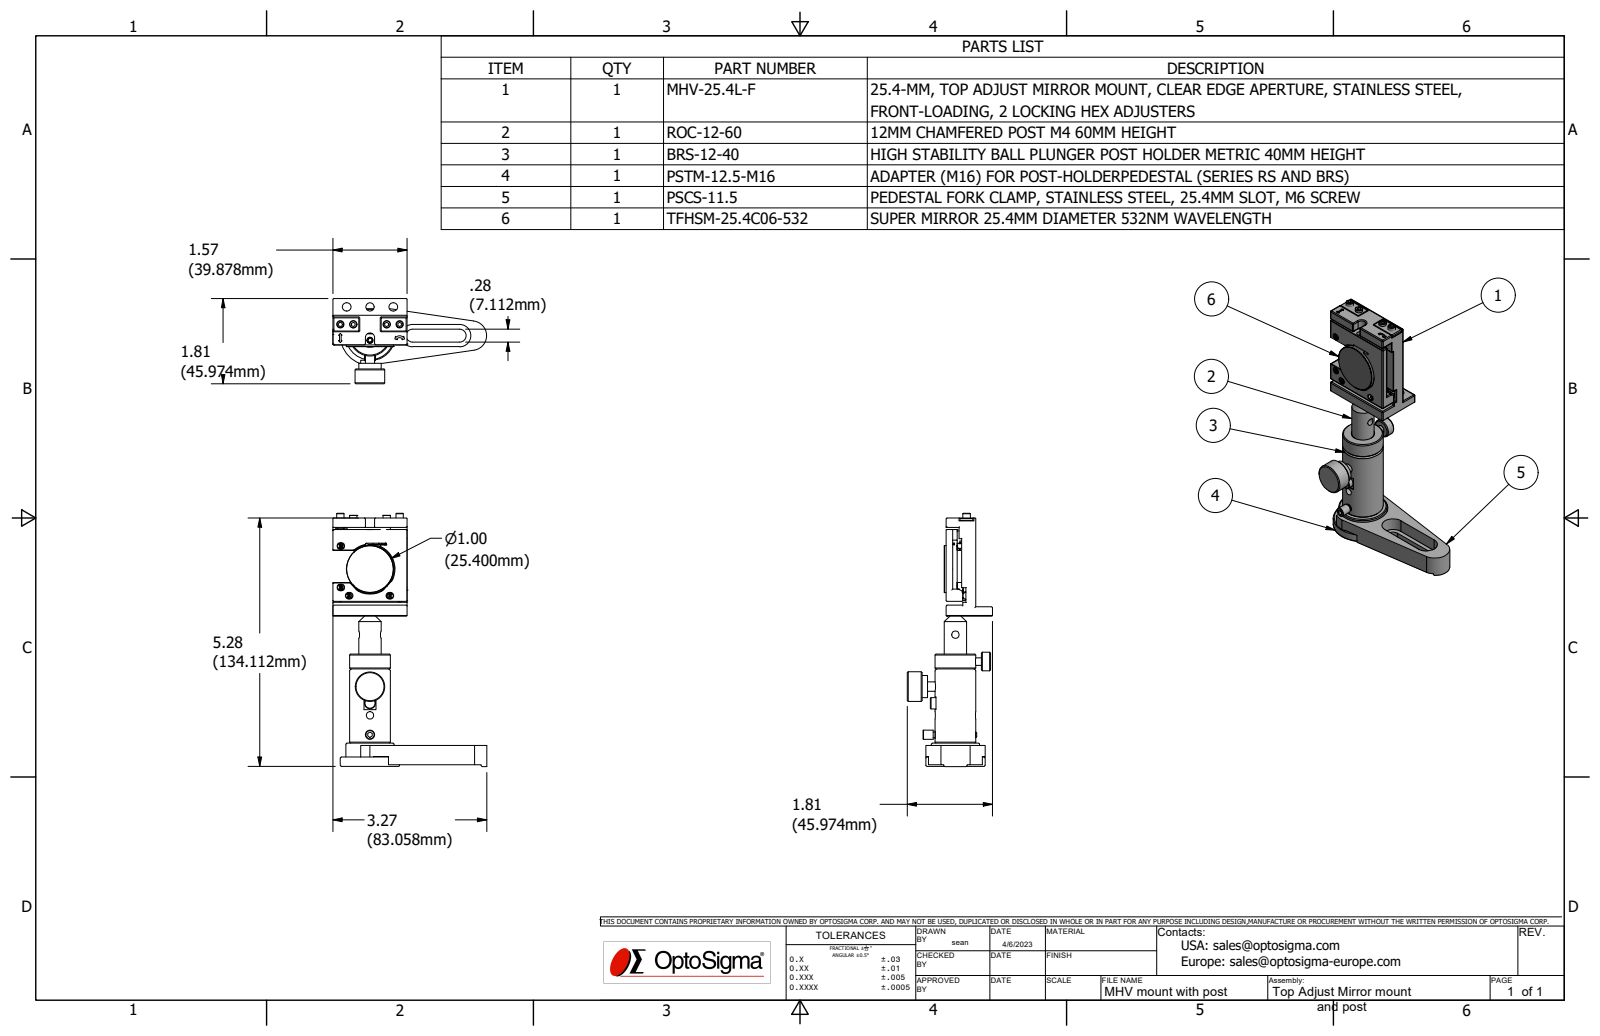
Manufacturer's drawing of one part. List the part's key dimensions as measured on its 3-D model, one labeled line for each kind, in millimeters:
Part name (STEP PRODUCT): Top adjust mirror holder and post; MHV25.4L-M02-21001-S01; MHV25.4L-M02-21001-S02; MHV25.4L-M02-21001-S03 (+7 more)
STEP written by: Autodesk Inventor 2022 (AUTOMOTIVE_DESIGN)
Units: millimetres
Bodies: 11 solids, 1036 faces (524 planar, 296 cylindrical, 216 other)
Overall size (bounding box): 136.7 × 83 × 46
Volume: 59 298 mm³ · Surface area: 33 793 mm²
Round holes (diameter × count): ⌀4 ×5, ⌀1 ×3, ⌀1.5 ×2, ⌀2 ×2, ⌀3.8 ×2, ⌀4.13 ×2, ⌀4.2 ×2, ⌀5.5 ×2, ⌀7 ×2, ⌀1.6 ×1, ⌀3 ×1, ⌀3.2 ×1
Round bosses / shafts (diameter × count): ⌀4 ×6, ⌀2.6 ×4, ⌀5 ×3, ⌀16 ×2, ⌀6.8 ×2, ⌀5.4 ×2, ⌀3 ×2, ⌀32 ×1
Partial cylindrical surfaces — rounded edges, fillets, slot ends (radius × count): R0.5 ×61, R0.2 ×51, R1.5 ×10, R4 ×9, R1 ×6, R2.25 ×4, R3.5 ×2, R6 ×2
Main face-to-face distances: 5, 16, 1, 6, 7, 11, 10, 9, 4, 8
Hole centre spacings: 6.95, 25, 7, 9.29, 10.82, 12.38, 12.5, 12.75
